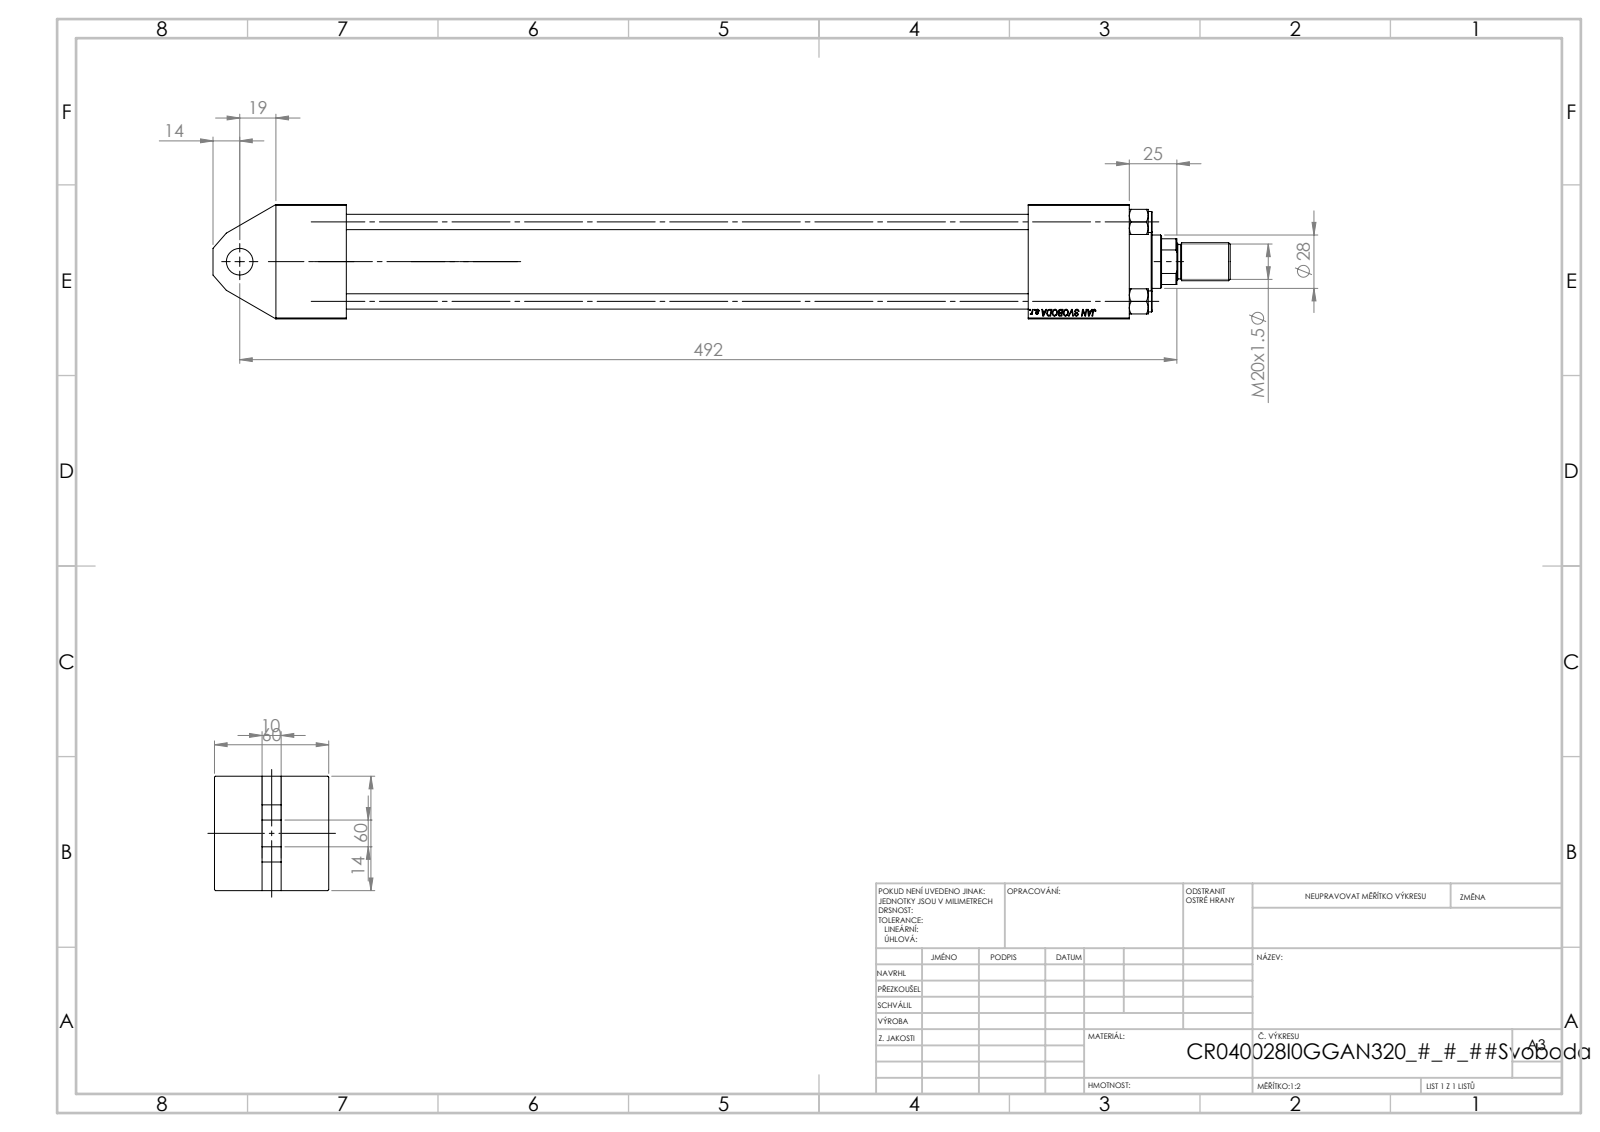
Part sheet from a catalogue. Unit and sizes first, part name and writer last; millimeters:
Units: millimetres
Overall size (bounding box): 534 × 60 × 60
Round holes (diameter × count): ⌀8 ×4, ⌀7 ×2, ⌀16.66 ×2, ⌀24 ×2, ⌀14 ×1, ⌀18.5 ×1, ⌀28 ×1, ⌀31 ×1, ⌀40 ×1, ⌀45 ×1
Round bosses / shafts (diameter × count): ⌀11 ×4, ⌀46 ×1, ⌀42 ×1, ⌀20 ×1, ⌀18 ×1
Partial cylindrical surfaces — rounded edges, fillets, slot ends (radius × count): R13.5 ×1
Main face-to-face distances: 60, 37, 25, 53, 35, 395, 358, 448, 411, 419.3
Hole centre spacings: 29.49, 41.7, 58.97, 392.5
Volume: 815 211 mm³ · Surface area: 255 718 mm²
Bodies: 12 solids, 1092 faces (506 planar, 84 cylindrical, 502 other)
Part name (STEP PRODUCT): V215CR_I_Body; V215_VC_A; V215CR_VCP_I; ROD_END_AH (+2 more)
STEP written by: SolidWorks 2019 (CONFIG_CONTROL_DESIGN)
